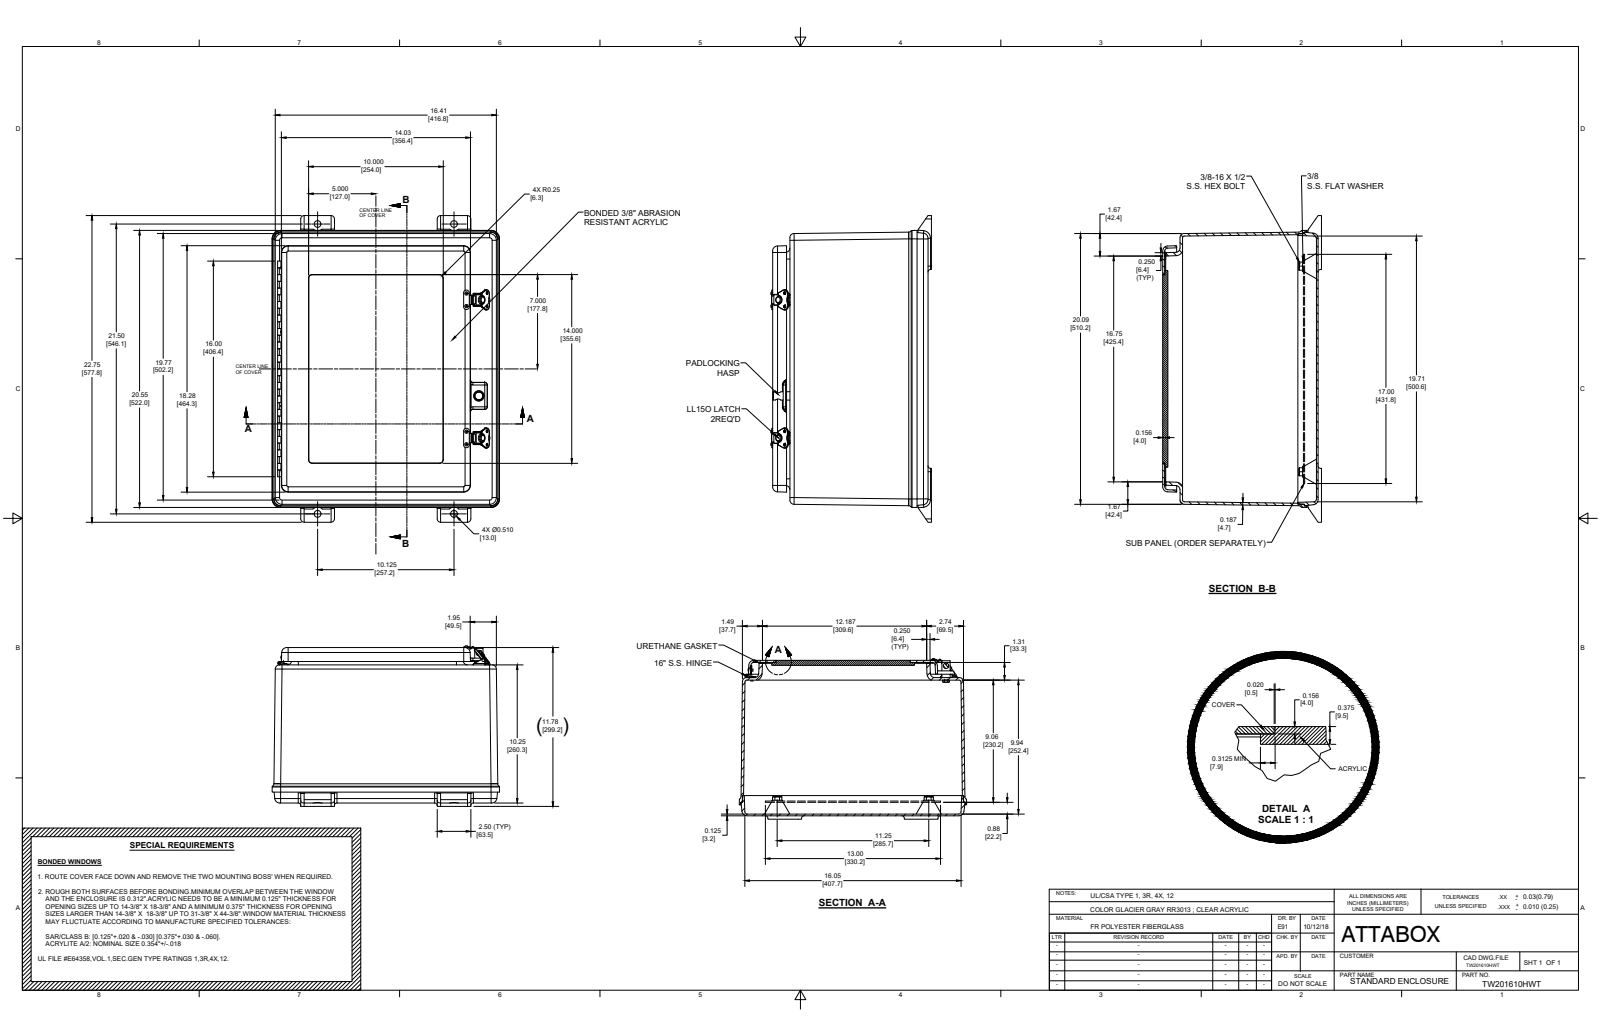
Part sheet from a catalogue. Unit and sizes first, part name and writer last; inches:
Units: inches
Overall size (bounding box): 22.75 × 16.875 × 11.909
Round holes (diameter × count): ⌀0.13 ×20, ⌀0.063 ×8, ⌀0.065 ×4, ⌀0.065 ×4, ⌀0.138 ×4, ⌀0.187 ×4, ⌀0.307 ×4, ⌀0.563 ×4, ⌀0.5 ×2, ⌀0.51 ×2, ⌀0.125 ×1, ⌀0.135 ×1
Round bosses / shafts (diameter × count): ⌀0.297 ×8, ⌀0.14 ×8, ⌀0.5 ×2, ⌀0.563 ×1, ⌀0.25 ×1, ⌀0.201 ×1, ⌀0.2 ×1, ⌀0.135 ×1
Partial cylindrical surfaces — rounded edges, fillets, slot ends (radius × count): R0.01 ×59, R0.25 ×28, R0.188 ×19, R0.5 ×12, R0.375 ×10, R0.03 ×8, R0.23 ×8, R0.187 ×6
Main face-to-face distances: 0.187, 0.125, 11.409, 11.535, 0.375, 11.159, 11.034, 0.156, 11.378, 11.253
Hole centre spacings: 10.25, 4.75, 1.526, 3.176, 10.25, 11.135, 13.619, 13.781
Volume: 320.5 in³ · Surface area: 3 456 in²
Bodies: 41 solids, 1179 faces (442 planar, 444 cylindrical, 293 other)
Part name (STEP PRODUCT): TW201610HWT
STEP written by: SolidWorks 2018 (AUTOMOTIVE_DESIGN)
